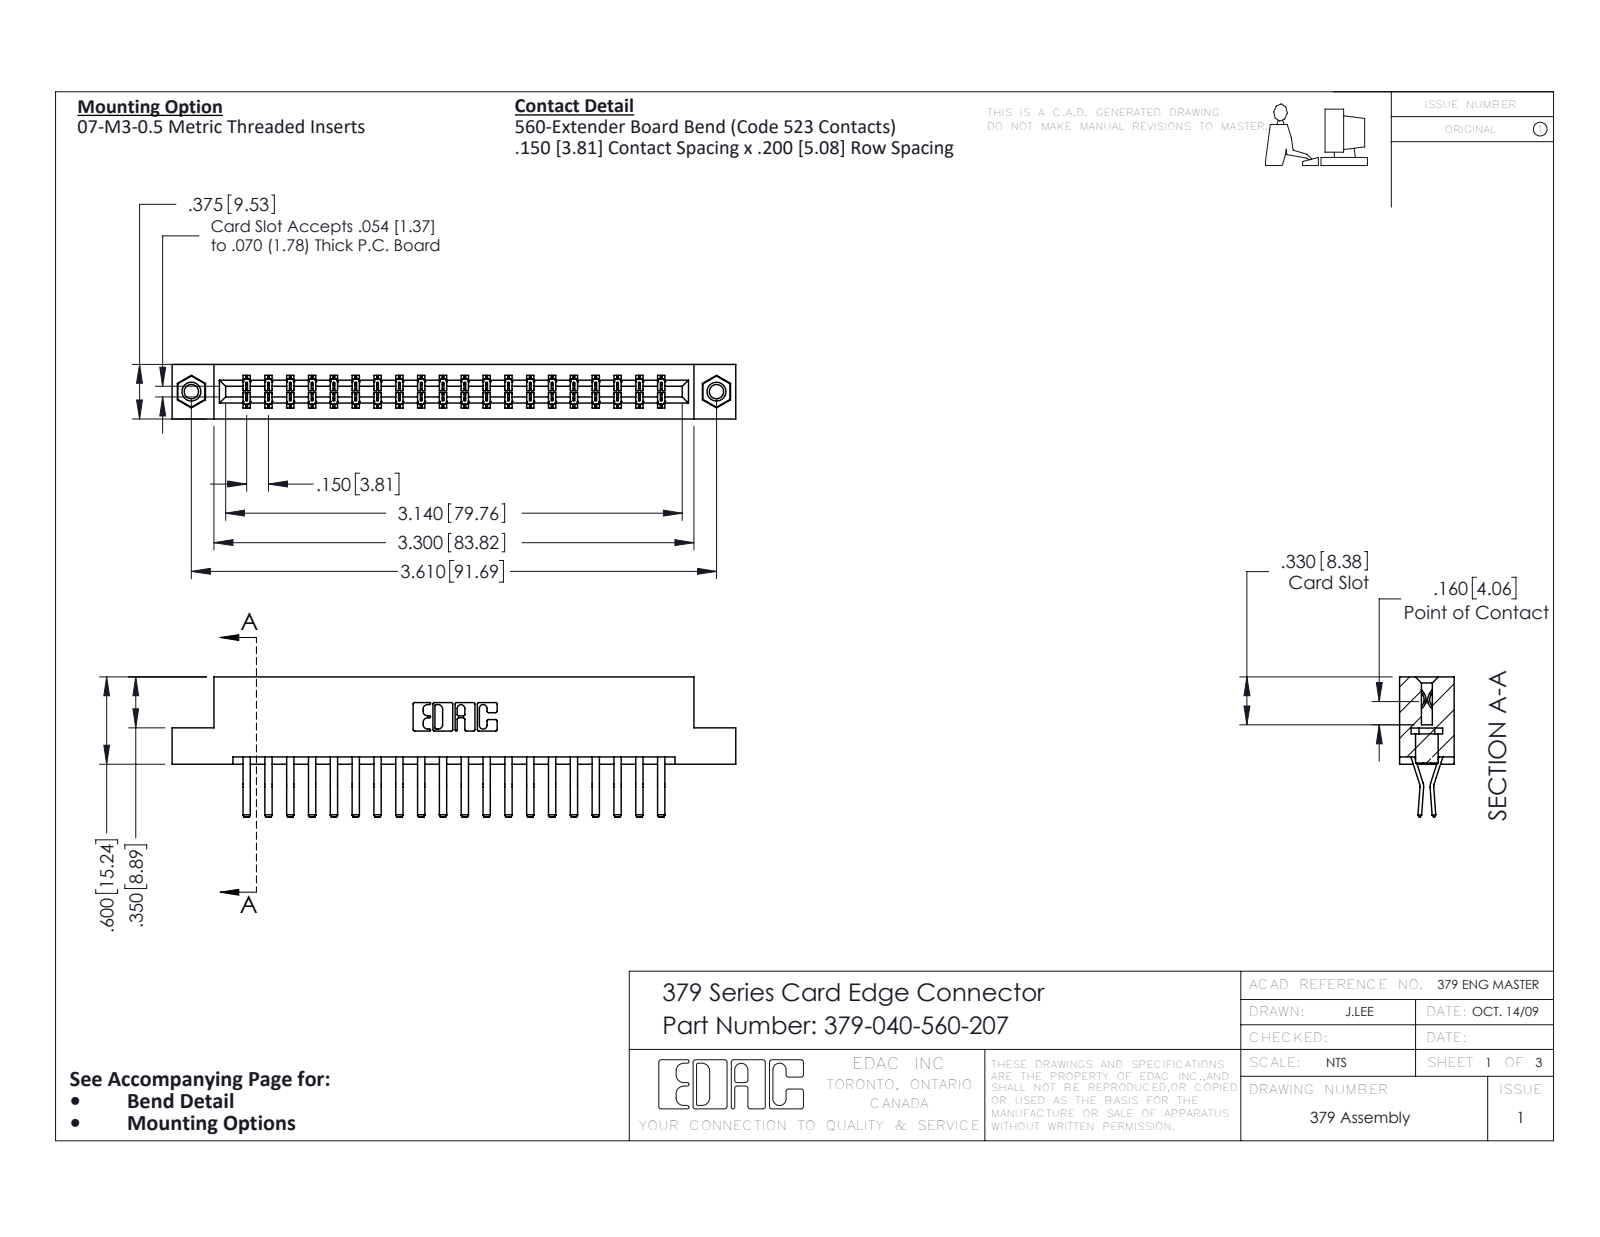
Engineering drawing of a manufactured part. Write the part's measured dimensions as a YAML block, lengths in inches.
part_name: "345-250-001_345-250-005-103; 379 Part_Flush - .156 Dia - TI; 379-040-560-207; 345-292-001_560 Tail"
step_written_by: "SolidWorks 2016 (CONFIG_CONTROL_DESIGN)"
units: inches
bodies: {solids: 43, faces: 2334, planar: 1542, cylindrical: 776, other: 16}
overall_size: [3.875, 0.962, 0.375]
volume: 0.638
surface_area: 19.13
round_holes:
  - {diameter: 0.098, count: 2}
  - {diameter: 0.125, count: 2}
  - {diameter: 0.156, count: 2}
round_bosses_or_shafts:
  - {diameter: 0.155, count: 2}
partial_cylinders:
  - {radius: 0.006, count: 60}
  - {radius: 0.01, count: 22}
  - {radius: 0.007, count: 6}
  - {radius: 0.031, count: 6}
  - {radius: 0.026, count: 3}
  - {radius: 0.01, count: 2}
  - {radius: 0.014, count: 2}
  - {radius: 0.022, count: 2}
face_to_face_distances: [0.3, 0.075, 0.375, 0.2, 0.15, 0.1, 0.6, 0.05, 0.55, 0.45]
hole_center_spacings: [3.61]
